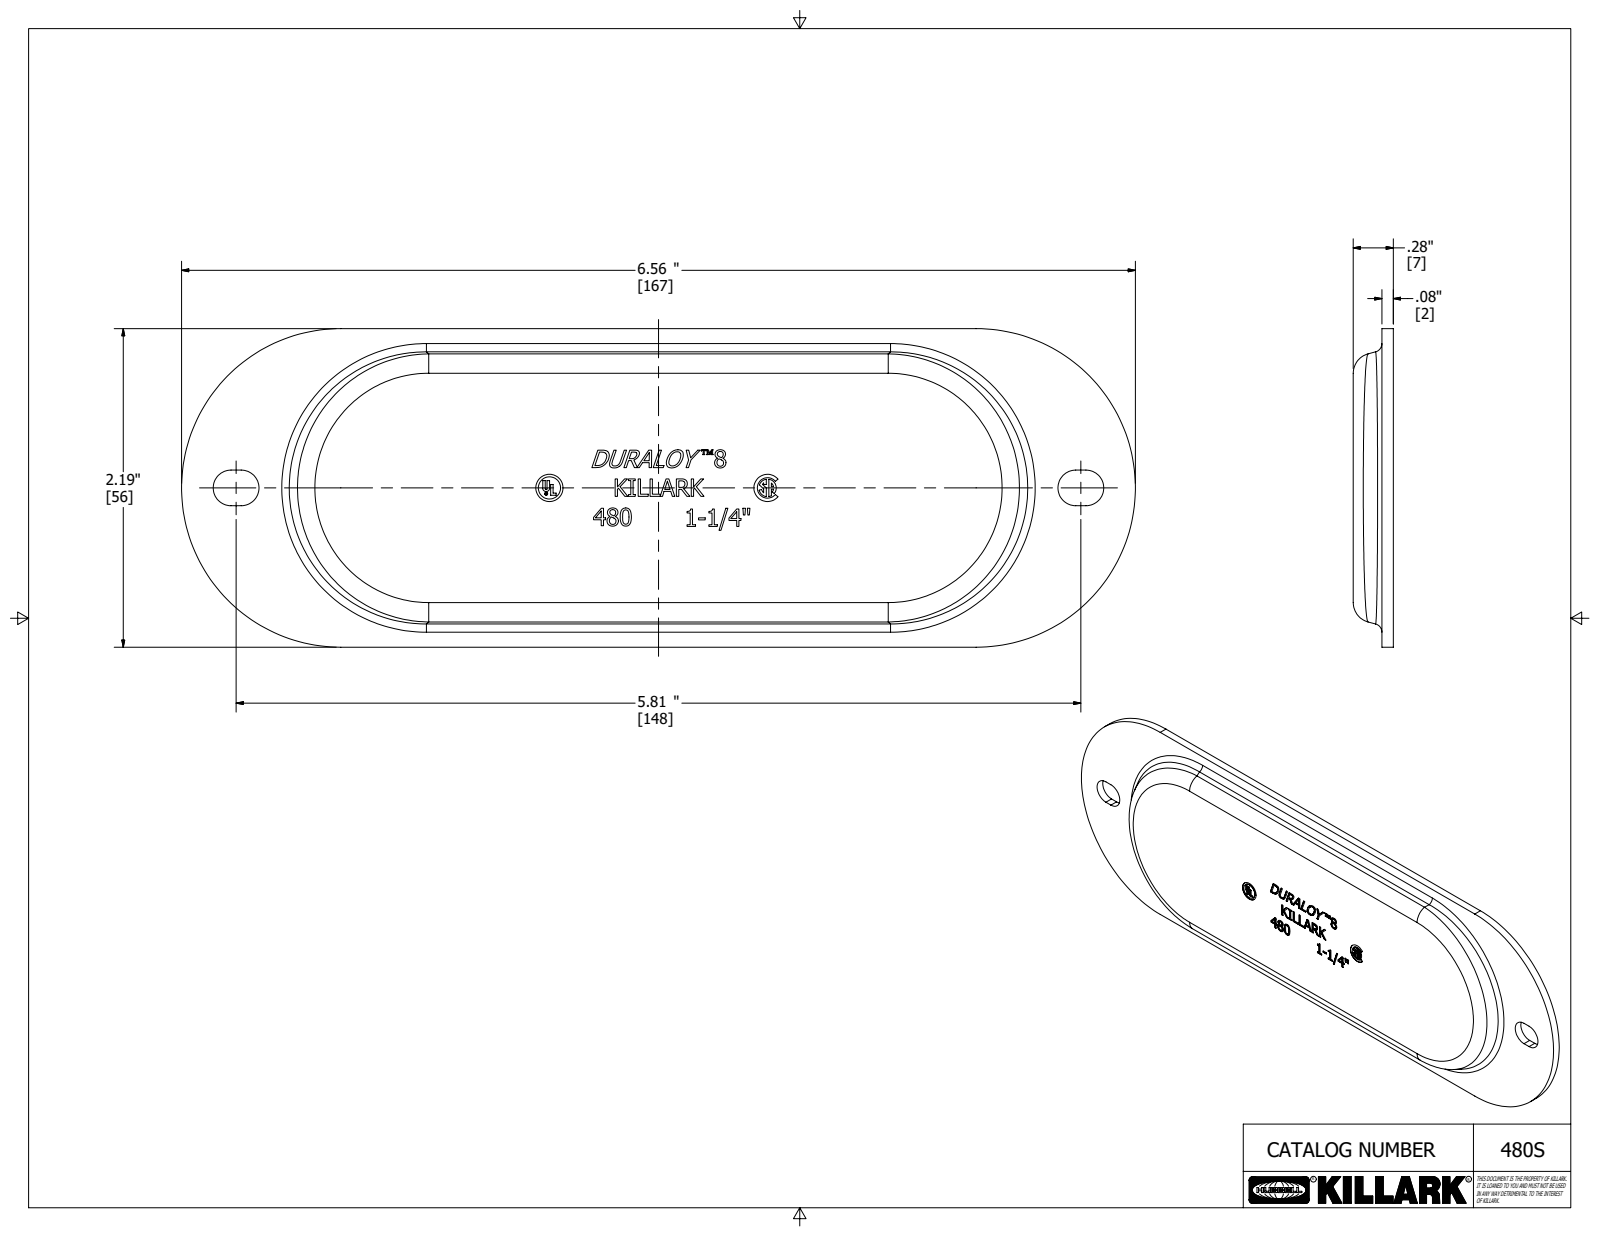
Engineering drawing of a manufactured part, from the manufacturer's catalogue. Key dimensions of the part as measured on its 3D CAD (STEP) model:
Part name (STEP PRODUCT): 21771
STEP written by: Autodesk Inventor 2018 (AUTOMOTIVE_DESIGN)
Units: inches
Bodies: 1 solid, 471 faces (320 planar, 32 cylindrical, 119 other)
Overall size (bounding box): 6.56 × 2.19 × 0.276
Volume: 1.136 in³ · Surface area: 30.26 in²
Round holes (diameter × count): ⌀0.021 ×1, ⌀0.187 ×1
Round bosses / shafts (diameter × count): ⌀0.153 ×1, ⌀0.017 ×1
Partial cylindrical surfaces — rounded edges, fillets, slot ends (radius × count): R0.059 ×4, R0.122 ×4, R0.138 ×4, R1.095 ×2, R0.006 ×1, R0.024 ×1, R0.042 ×1, R0.06 ×1
Main face-to-face distances: 0.079, 0.197, 0.276, 0.118, 2.19, 0.078, 0.274, 0.196, 0.972, 1.217
Hole centre spacings: 0.046
